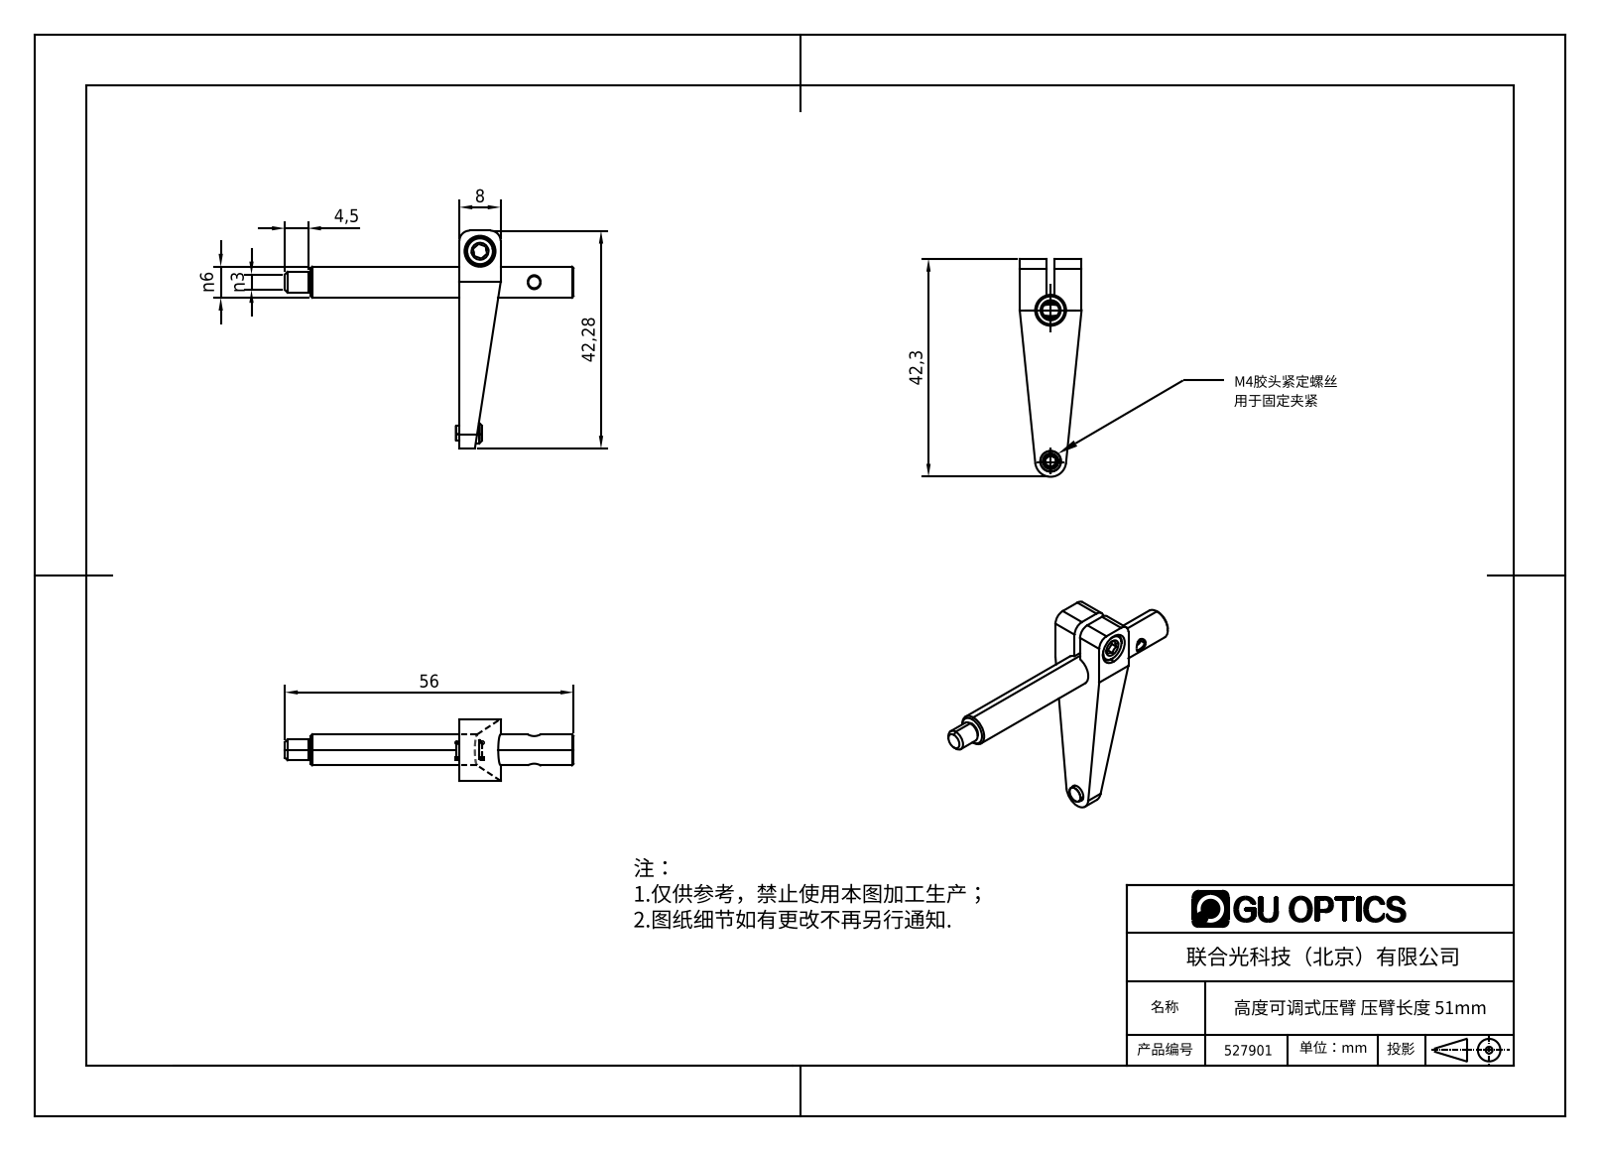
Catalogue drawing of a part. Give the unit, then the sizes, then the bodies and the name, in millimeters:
Units: millimetres
Overall size (bounding box): 56 × 42.3 × 12
Round holes (diameter × count): ⌀3.3 ×2, ⌀2.3 ×1, ⌀2.8 ×1, ⌀6 ×1
Round bosses / shafts (diameter × count): ⌀4 ×2, ⌀6 ×1, ⌀3.2 ×1, ⌀3 ×1
Partial cylindrical surfaces — rounded edges, fillets, slot ends (radius × count): R2 ×2, R3 ×1
Main face-to-face distances: 5.25, 6.75, 8, 1.5, 12, 4.85, 28.87, 36.87, 11.6, 6.35
Hole centre spacings: 12.1, 29.3
Bodies: 0 solids, 81 faces (34 planar, 25 cylindrical, 22 other)
Part name (STEP PRODUCT): 1.8.3.5_ZFJ-E_标准大号可调节压臂，M4螺纹接杆，A
STEP written by: SolidWorks 2018 (AUTOMOTIVE_DESIGN)
